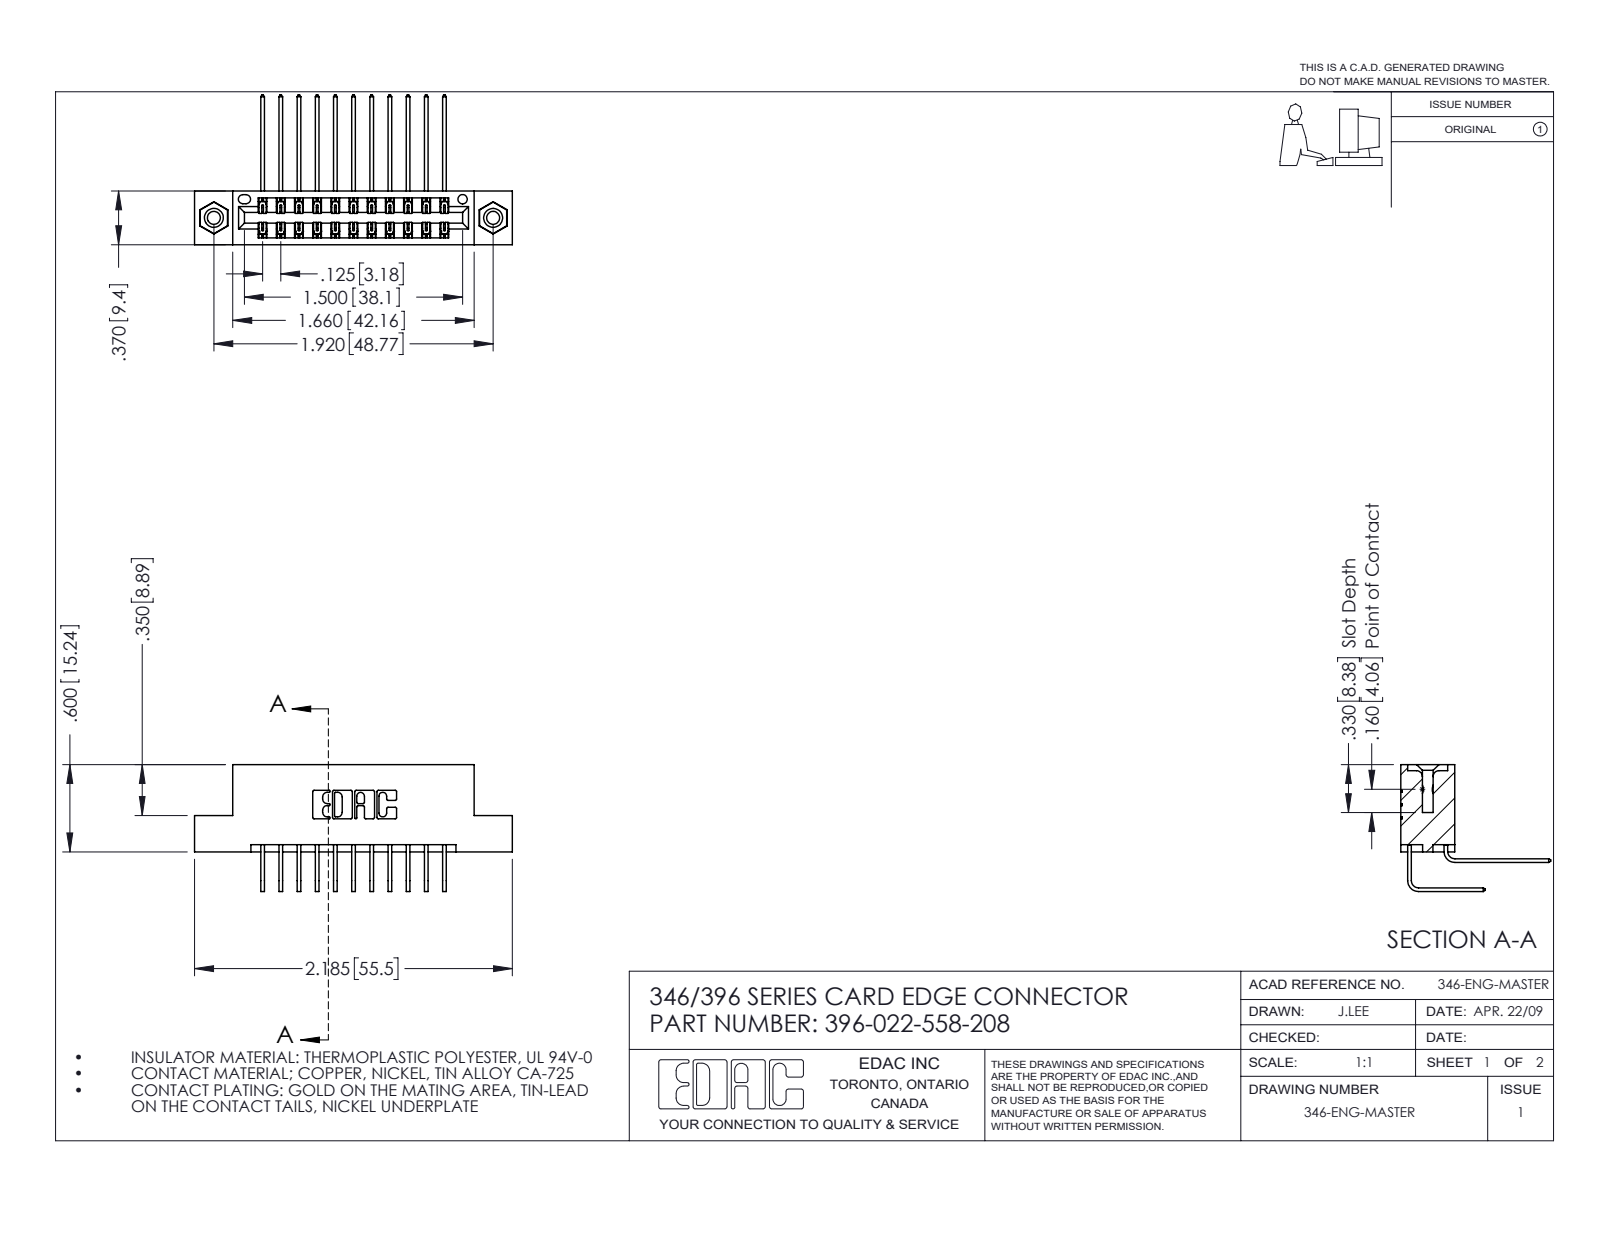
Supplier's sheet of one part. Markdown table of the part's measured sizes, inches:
| quantity | value |
| --- | --- |
| part name | 346 Part_Flush Mounting Lugs - 0.156 Dia-TI; 345-292-001_558 Tail - 2; 345-250-001_345-250-003-102; 396-022-558-208 (+1 more) |
| STEP written by | SolidWorks 2016 (CONFIG_CONTROL_DESIGN) |
| units | inches |
| bodies | 25 solids, 1370 faces (922 planar, 432 cylindrical, 16 other) |
| overall size | 2.185 × 1.03 × 0.873 |
| volume | 0.323 in³ |
| surface area | 11.49 in² |
| round holes (diameter × count) | 0.089 × 2, 0.125 × 2, 0.156 × 2, 0.064 × 1 |
| round bosses / shafts (diameter × count) | 0.155 × 2 |
| partial cylindrical surfaces (radius × count) | 0.006 × 33, 0.01 × 22, 0.007 × 6, 0.031 × 6, 0.026 × 3, 0.014 × 2, 0.022 × 2, 0.024 × 2 |
| main face-to-face distances | 0.322, 0.25, 0.048, 0.37, 0.025, 0.298, 0.072, 0.275, 0.148, 0.222 |
| hole center spacings | 0.246, 1.715, 1.92 |
